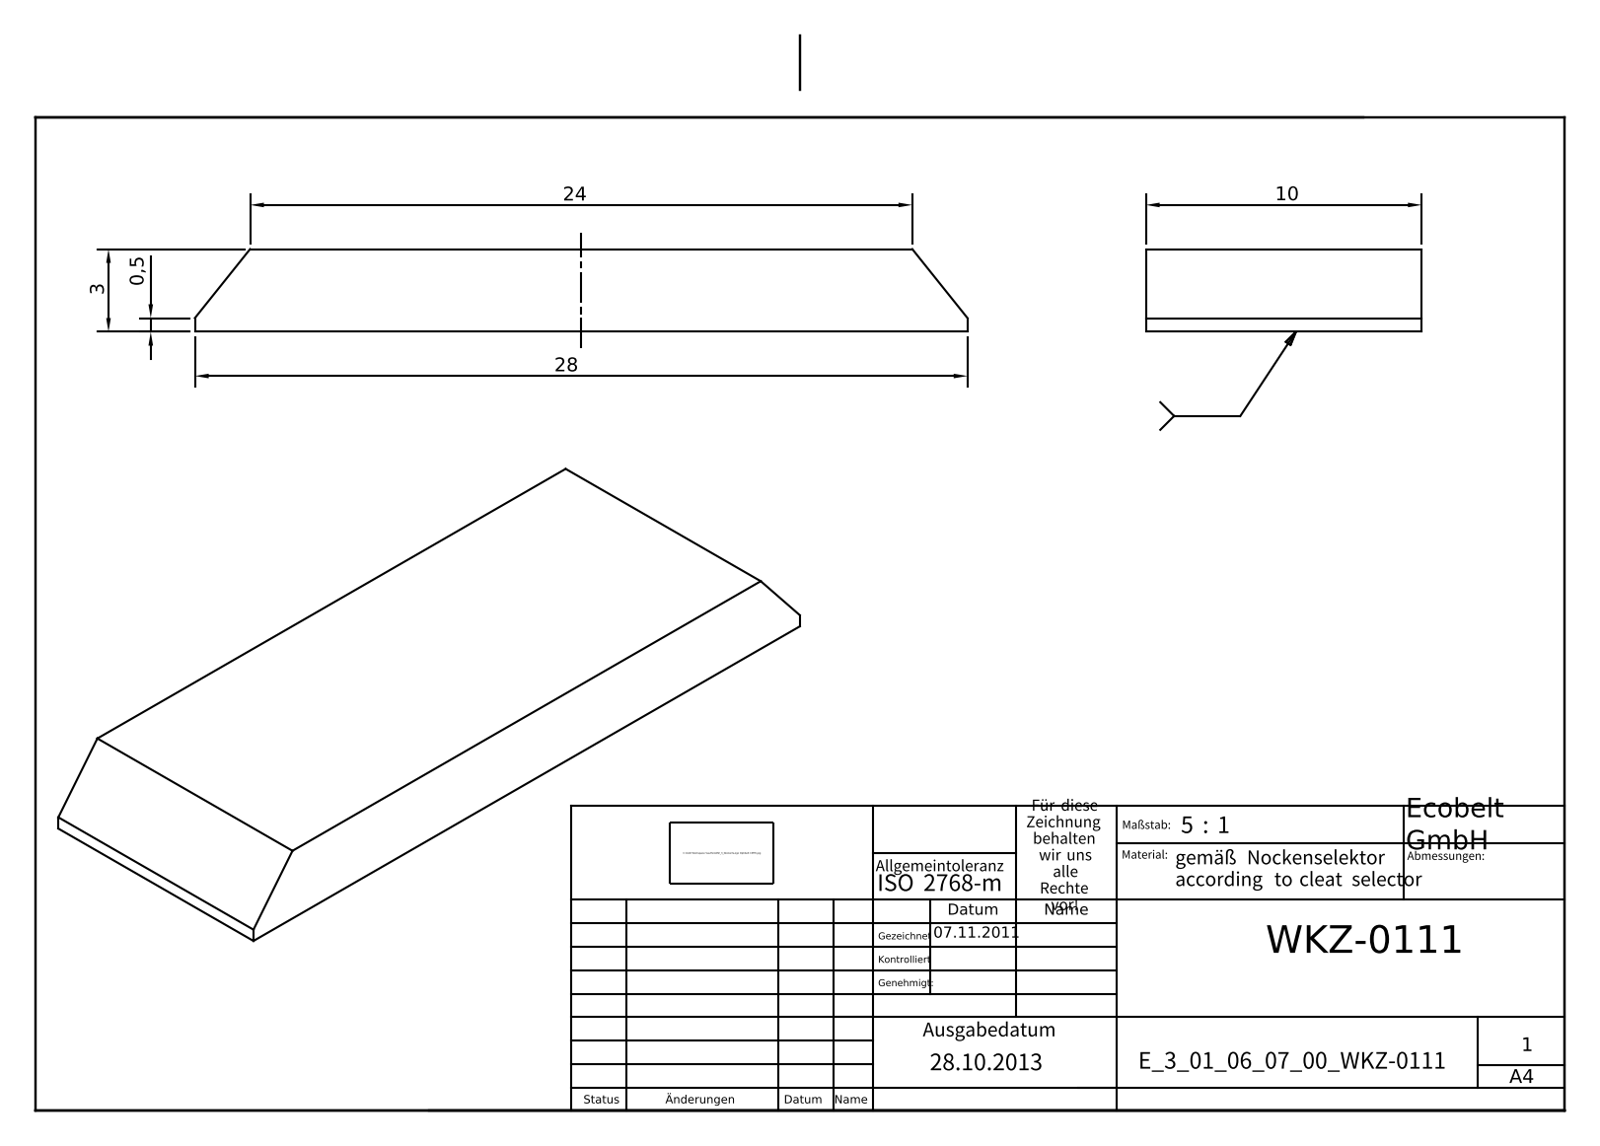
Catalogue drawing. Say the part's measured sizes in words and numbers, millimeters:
The part is named "E_3_01_06_07_00_WKZ-0111". Its 3-D file was written by "Autodesk Inventor 2025 (AUTOMOTIVE_DESIGN)". It is 1 solid with 8 faces: 8 planar, 0 cylindrical and 0 other. Overall it measures 28 by 10 by 3 millimeters. Its volume is 790 cubic millimeters and its surface area 752 square millimeters. The main face-to-face distances are 3, 10, 28.
